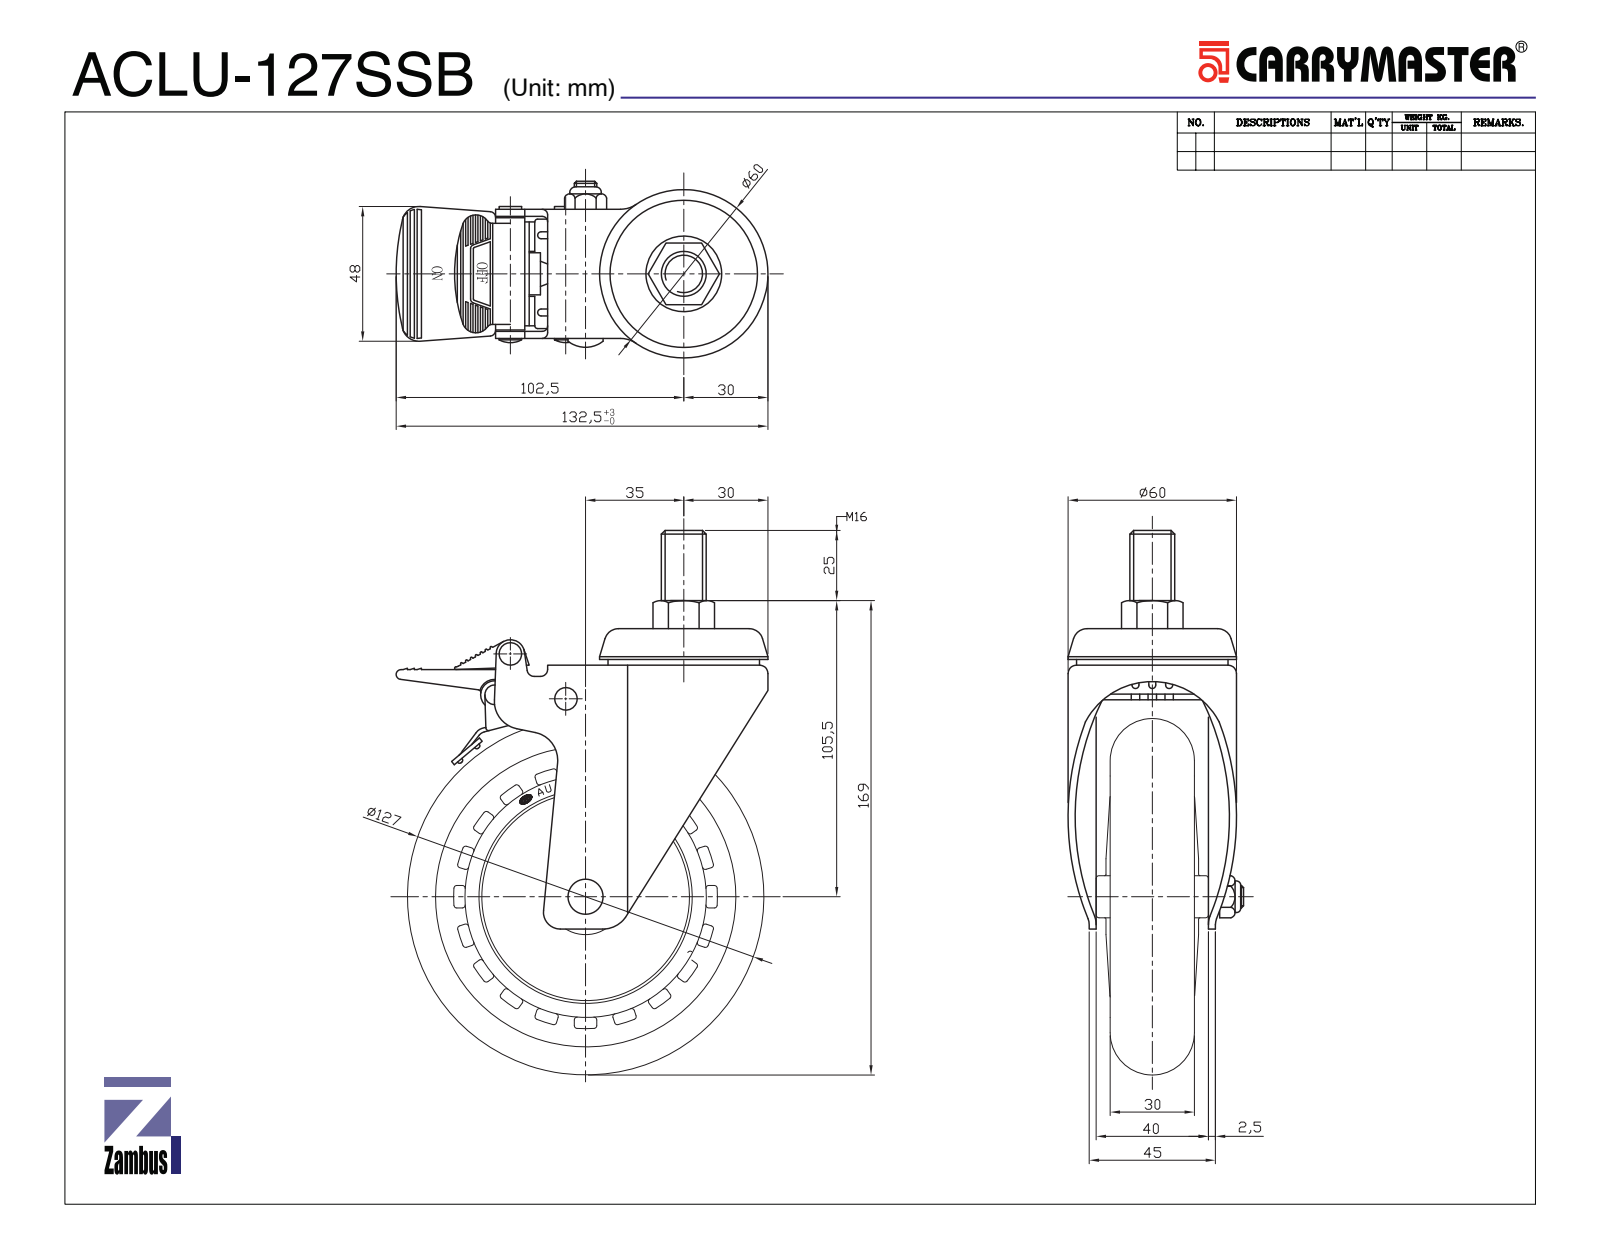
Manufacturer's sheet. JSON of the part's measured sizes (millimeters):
{"part_name": "ACLU-127 CORE; ACLU-100SSB PIN-A; 6-35GANGQIU-X20-15; 6-35GANGQIU-X20-2 (+8 more)", "step_written_by": "SolidWorks 2018 (CONFIG_CONTROL_DESIGN)", "units": "millimeters", "bodies": {"solids": 45, "faces": 1669, "planar": 827, "cylindrical": 486, "other": 356}, "overall_size": [196.02, 134.83, 60], "volume_mm3": 403316, "surface_area_mm2": 168013, "round_holes": [[3.5, 2], [4.3, 2], [5.2, 2], [5.3, 1], [6.8, 1], [8, 1], [9.6, 1], [12.6, 1], [14, 1], [19.6, 1], [22, 1], [28.62, 1]], "round_bosses_or_shafts": [[9, 2], [4.9, 2], [108, 1], [73, 1], [59.7, 1], [40, 1], [31, 1], [28, 1]], "partial_cylinders_radius": [[1, 82], [0.2, 20], [3.86, 19], [25, 16], [2, 6], [7, 5], [2.5, 4], [3, 4]], "face_to_face_distances": [2.5, 8, 30, 5.5, 38, 11.8, 35.5, 17.3, 43.5, 19.8], "hole_center_spacings": [17.48, 9.7, 12.81, 25.75, 26.08, 70.54, 76.64, 77.59]}
